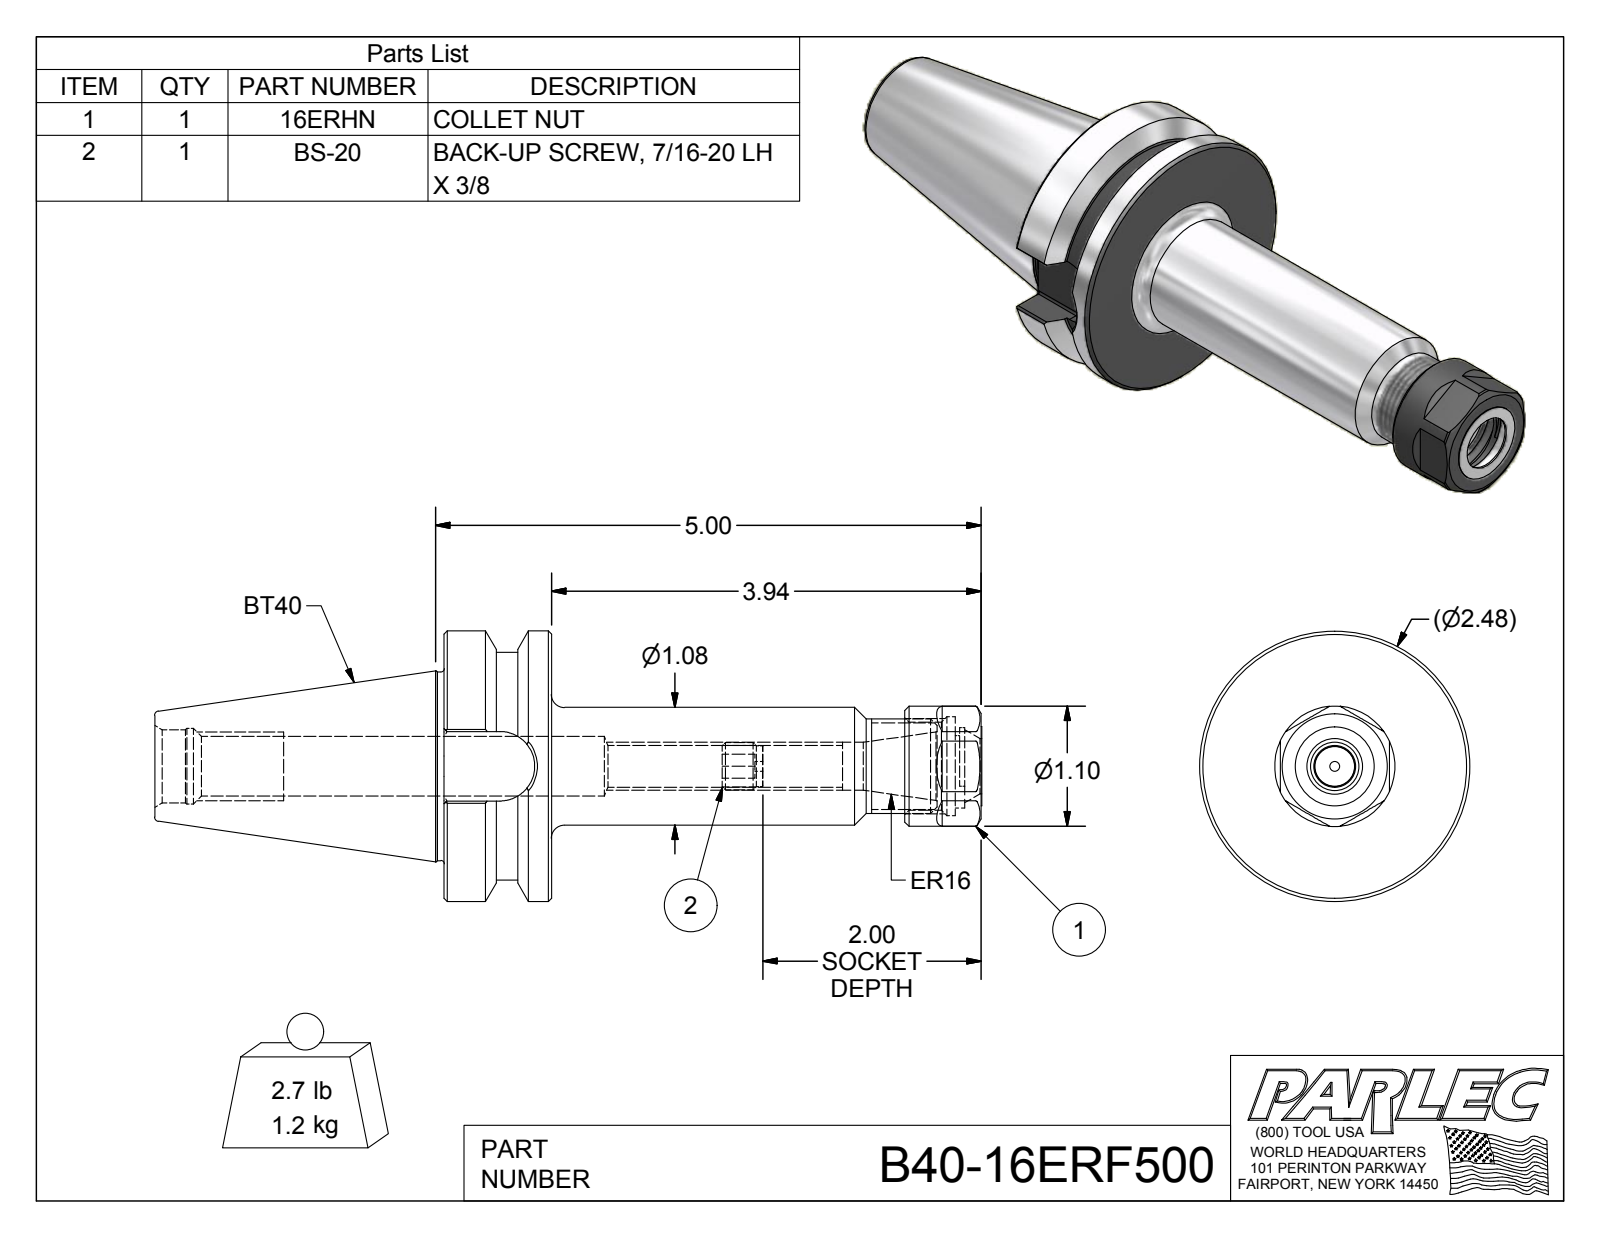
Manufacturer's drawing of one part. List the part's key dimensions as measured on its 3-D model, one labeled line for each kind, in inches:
Part name (STEP PRODUCT): B40-16ER5-1; 16ERHN; BS-20; B40-16ERF500
STEP written by: Autodesk Inventor 2016 (AUTOMOTIVE_DESIGN)
Units: inches
Bodies: 3 solids, 121 faces (50 planar, 33 cylindrical, 38 other)
Overall size (bounding box): 7.575 × 2.48 × 2.48
Volume: 10.08 in³ · Surface area: 56.99 in²
Round holes (diameter × count): ⌀0.09 ×1, ⌀0.383 ×1, ⌀0.44 ×1, ⌀0.488 ×1, ⌀0.545 ×1, ⌀0.67 ×1, ⌀0.67 ×1, ⌀0.694 ×1, ⌀0.807 ×1, ⌀0.906 ×1
Round bosses / shafts (diameter × count): ⌀2.48 ×1, ⌀2.087 ×1, ⌀1.73 ×1, ⌀1.102 ×1, ⌀1.08 ×1, ⌀0.866 ×1, ⌀0.432 ×1, ⌀0.372 ×1
Partial cylindrical surfaces — rounded edges, fillets, slot ends (radius × count): R0.02 ×8, R0.285 ×1, R0.319 ×1, R0.354 ×1
Main face-to-face distances: 0.984, 4.922, 3.938, 0.99, 1.78, 0.395, 1.385, 4.698, 3.714, 0.224
Hole centre spacings: 0.06
